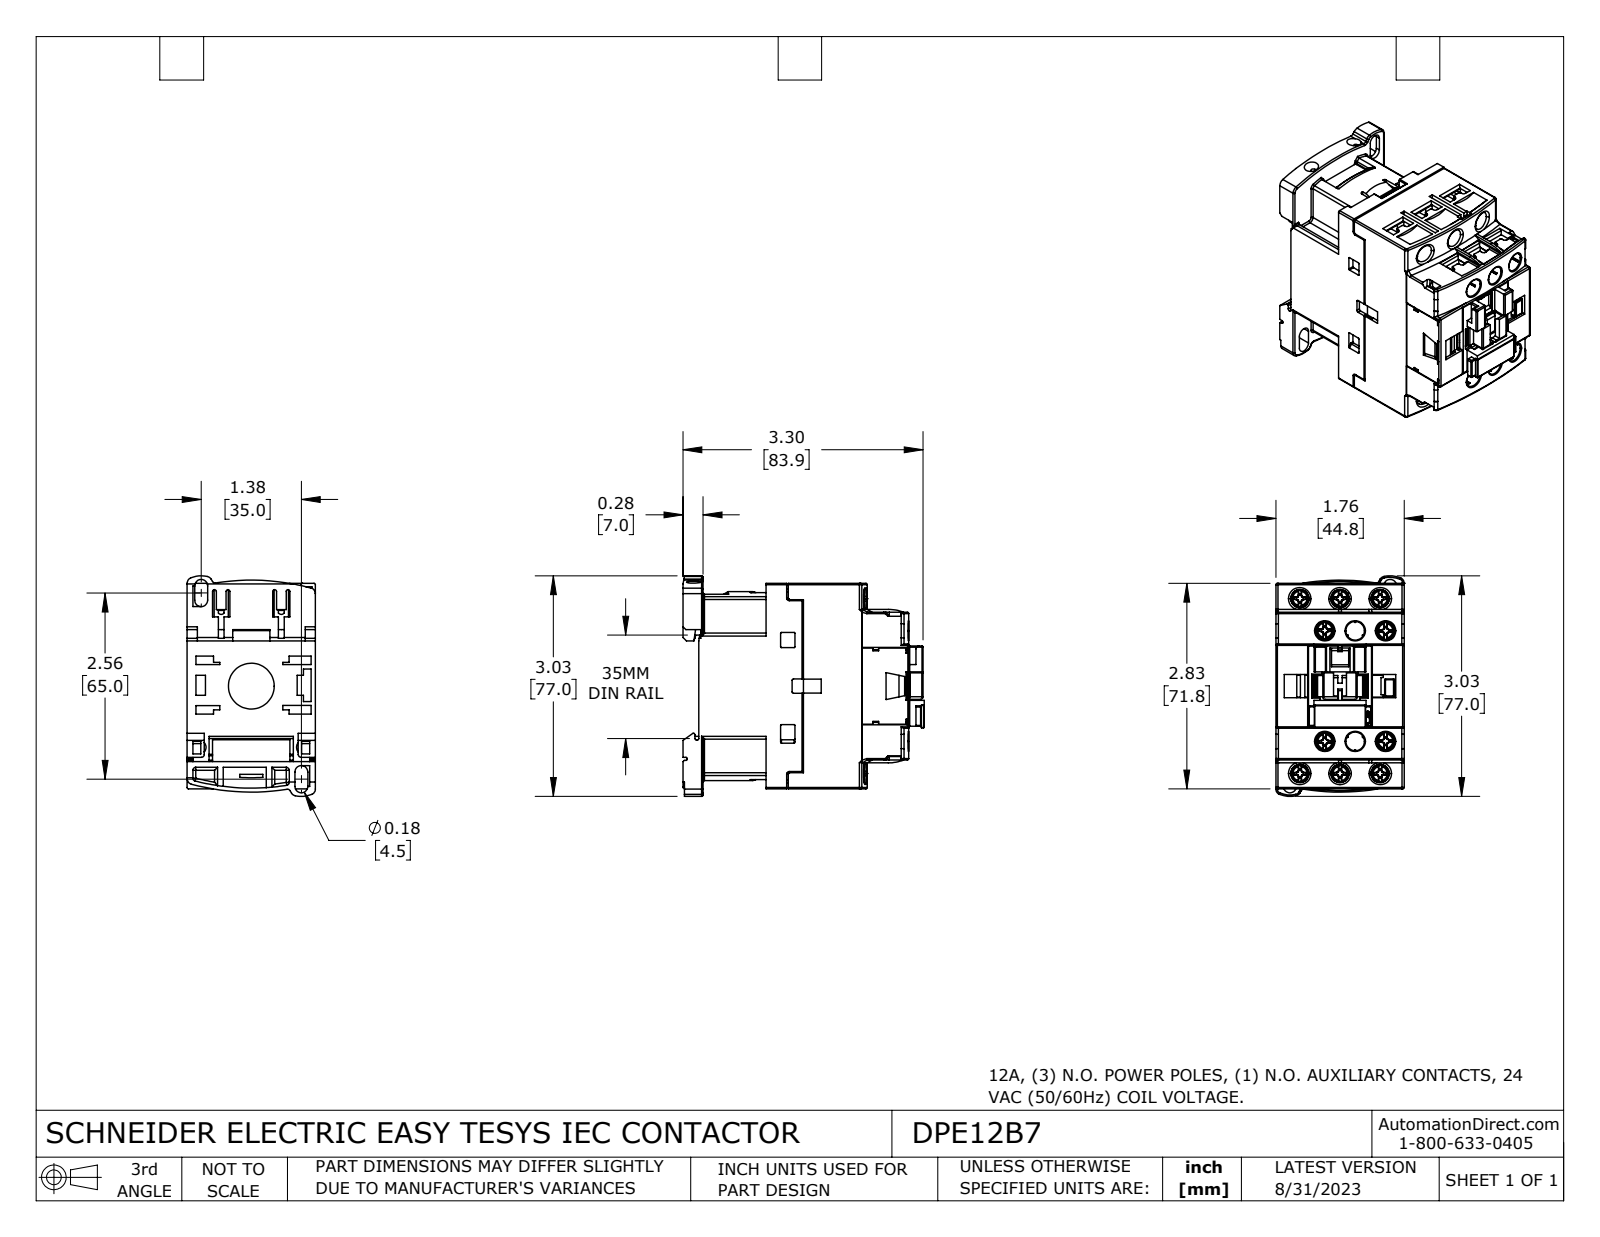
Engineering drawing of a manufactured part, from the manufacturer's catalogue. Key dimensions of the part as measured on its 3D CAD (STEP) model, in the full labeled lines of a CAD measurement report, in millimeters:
Part name (STEP PRODUCT): DPE12B7
STEP written by: SolidWorks 2021 (CONFIG_CONTROL_DESIGN)
Units: millimetres
Bodies: 20 solids, 3363 faces (2297 planar, 694 cylindrical, 372 other)
Overall size (bounding box): 84.3 × 77 × 45.3
Volume: 146 000 mm³ · Surface area: 66 710 mm²
Round holes (diameter × count): ⌀6.4 ×6, ⌀6.5 ×6, ⌀5 ×2, ⌀4.2 ×1, ⌀16 ×1
Round bosses / shafts (diameter × count): ⌀3.5 ×10, ⌀2.7 ×10, ⌀8 ×6
Partial cylindrical surfaces — rounded edges, fillets, slot ends (radius × count): R0.5 ×78, R0.3 ×64, R1 ×61, R0.2 ×42, R0.4 ×24, R16 ×9, R0.6 ×8, R2 ×7
Main face-to-face distances: 1.2, 44.8, 43.6, 8.2, 28.7, 20.5, 8.9, 70.6, 34.7, 28.4
Hole centre spacings: 10.6, 12.4, 14, 14.2, 20, 22.3, 33.6, 40
